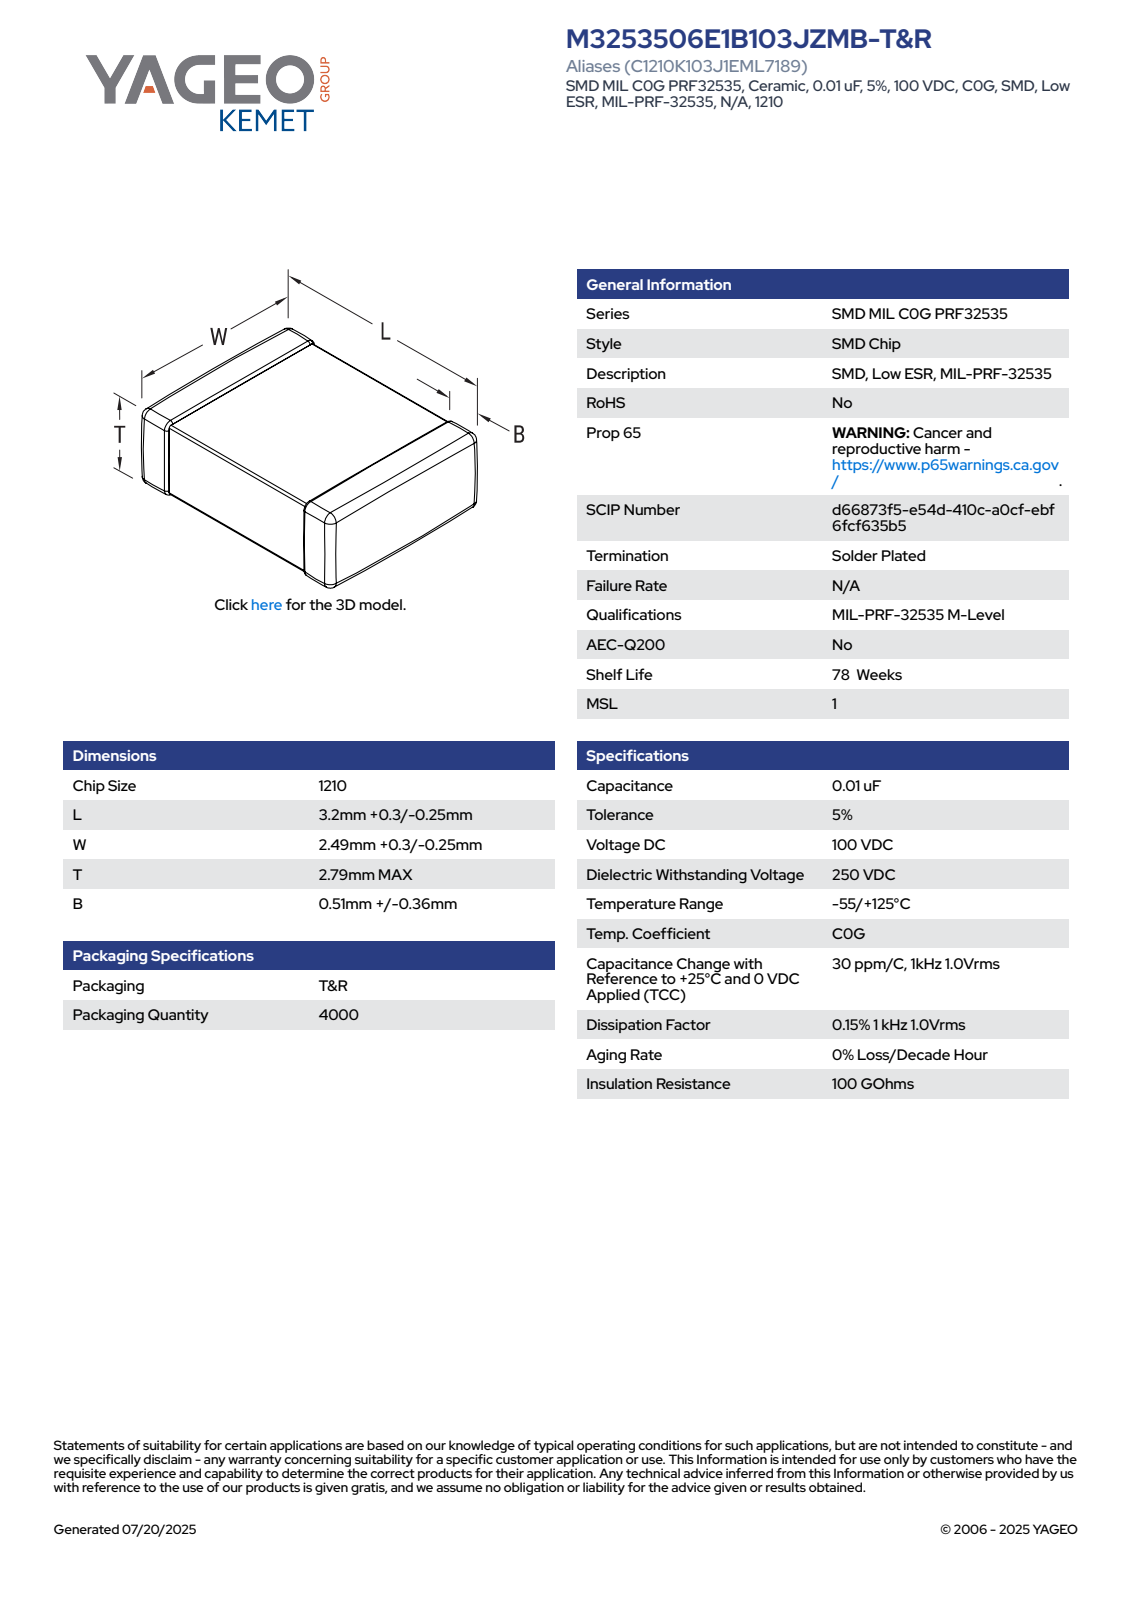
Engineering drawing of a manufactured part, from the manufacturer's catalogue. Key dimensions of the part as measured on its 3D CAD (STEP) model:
Part name (STEP PRODUCT): CCS_STDNOS_1210_L3.5W2.79T2.79B0.51
STEP written by: SolidWorks 2021 (AUTOMOTIVE_DESIGN)
Units: millimetres
Bodies: 4 solids, 129 faces (71 planar, 42 cylindrical, 16 other)
Overall size (bounding box): 3.5 × 2.79 × 2.79
Volume: 26 mm³ · Surface area: 54 mm²
Main face-to-face distances: 2.67, 2.73, 3.5, 2.79, 2.74, 2.68, 1.27, 1.46, 1.54, 1.19
